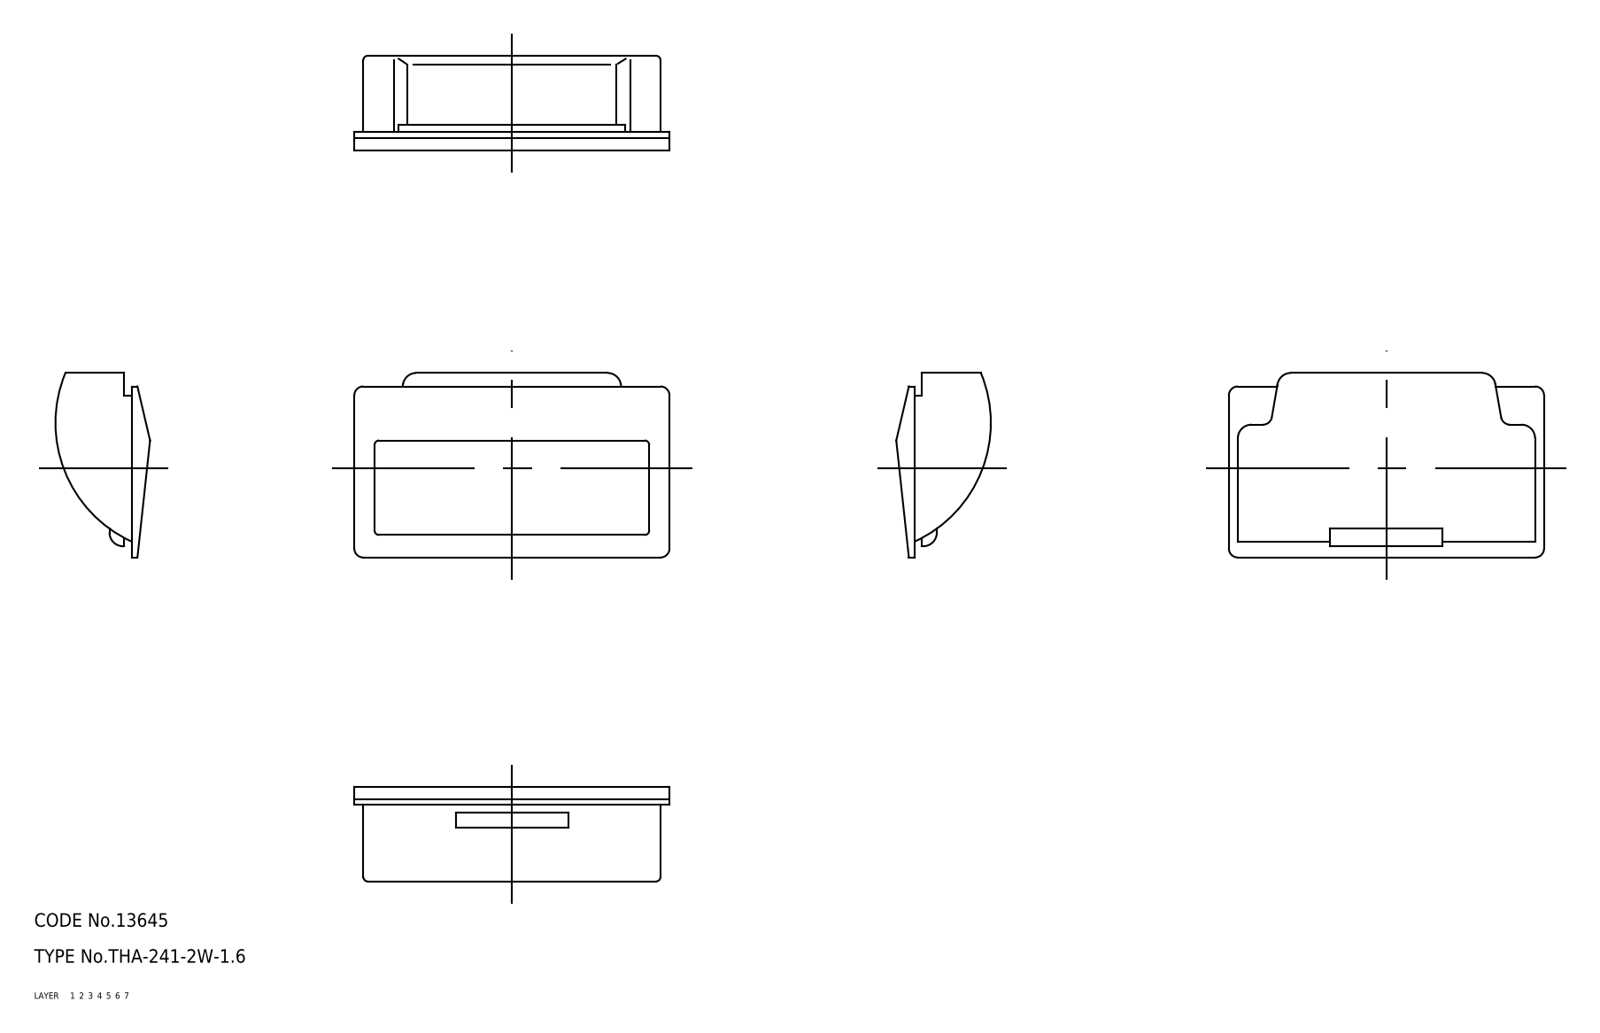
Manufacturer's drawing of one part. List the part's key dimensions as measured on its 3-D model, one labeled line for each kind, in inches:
Part name (STEP PRODUCT): pull; THA_241_2W_1_6
STEP written by: SolidWorks 2015 (AUTOMOTIVE_DESIGN)
Units: inches
Bodies: 1 solid, 82 faces (31 planar, 31 cylindrical, 20 other)
Overall size (bounding box): 2.756 × 1.614 × 0.827
Volume: 0.865 in³ · Surface area: 18.2 in²
Partial cylindrical surfaces — rounded edges, fillets, slot ends (radius × count): R0.039 ×17, R0.079 ×8, R0.118 ×3, R1.063 ×1, R1.142 ×1, R1.155 ×1
Main face-to-face distances: 0.079, 0.512, 0.098, 2.5, 0.335, 0.433, 2.165, 2.067, 0.069, 2.598
